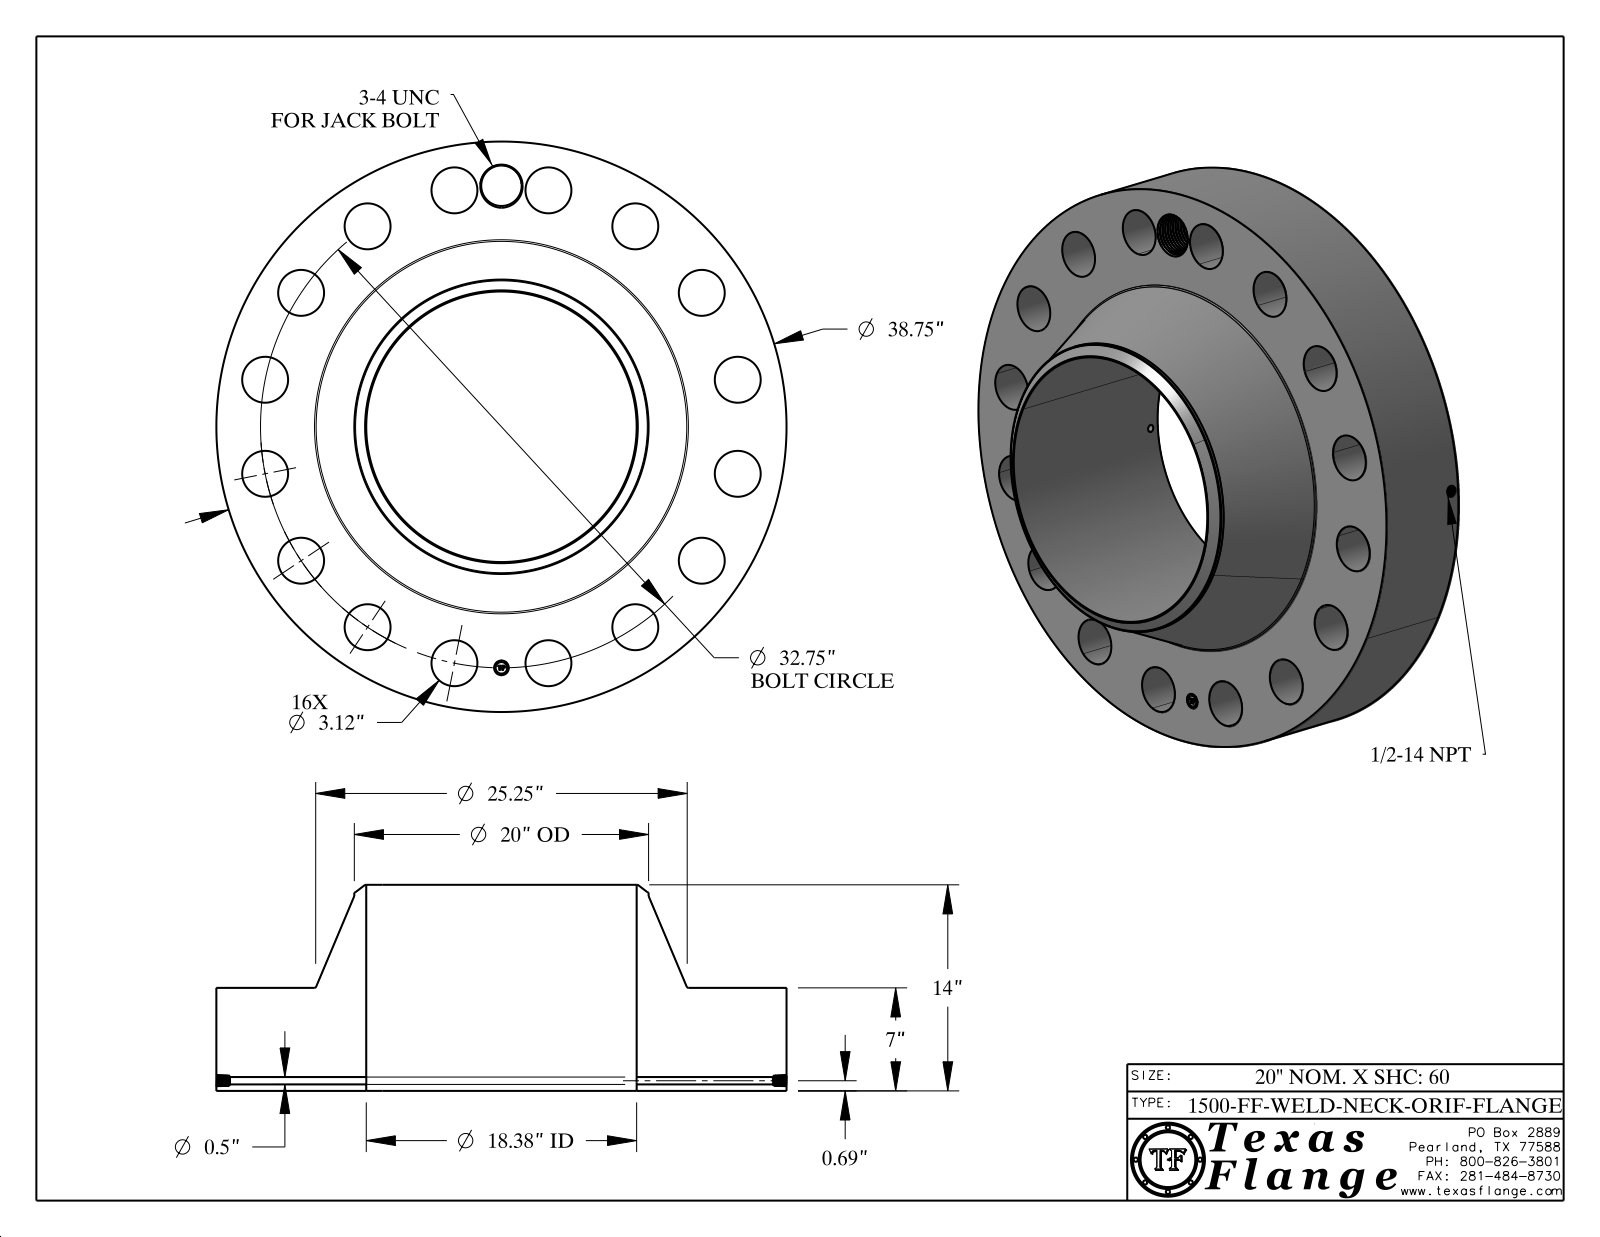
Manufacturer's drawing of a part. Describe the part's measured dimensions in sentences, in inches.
The part is named "1500-FF-WELD-NECK". Its 3-D file was written by "CATIA V5 STEP AP214 (AUTOMOTIVE_DESIGN)". It is 1 solid with 864 faces: 368 planar, 134 cylindrical and 362 other. Overall it measures 38.75 by 38.75 by 14 inches. Its volume is 6 382 cubic inches and its surface area 4 772 square inches. Round holes: 16 of diameter 3.12, 1 of diameter 0.5, 1 of diameter 0.672, 1 of diameter 1, 1 of diameter 2.75, 1 of diameter 18.376. Round bosses or shafts: 8 of diameter 0.061, 1 of diameter 38.75, 1 of diameter 20, 1 of diameter 0.788. The main face-to-face distances are 7, 14, 0.015, 6.985, 7.015, 0.298, 0.292, 0.054, 0.248, 0.193. The hole center spacings are 30.257, 18.195, 27.231, 32.12, 16.375, 6.389, 6.389, 12.533.
